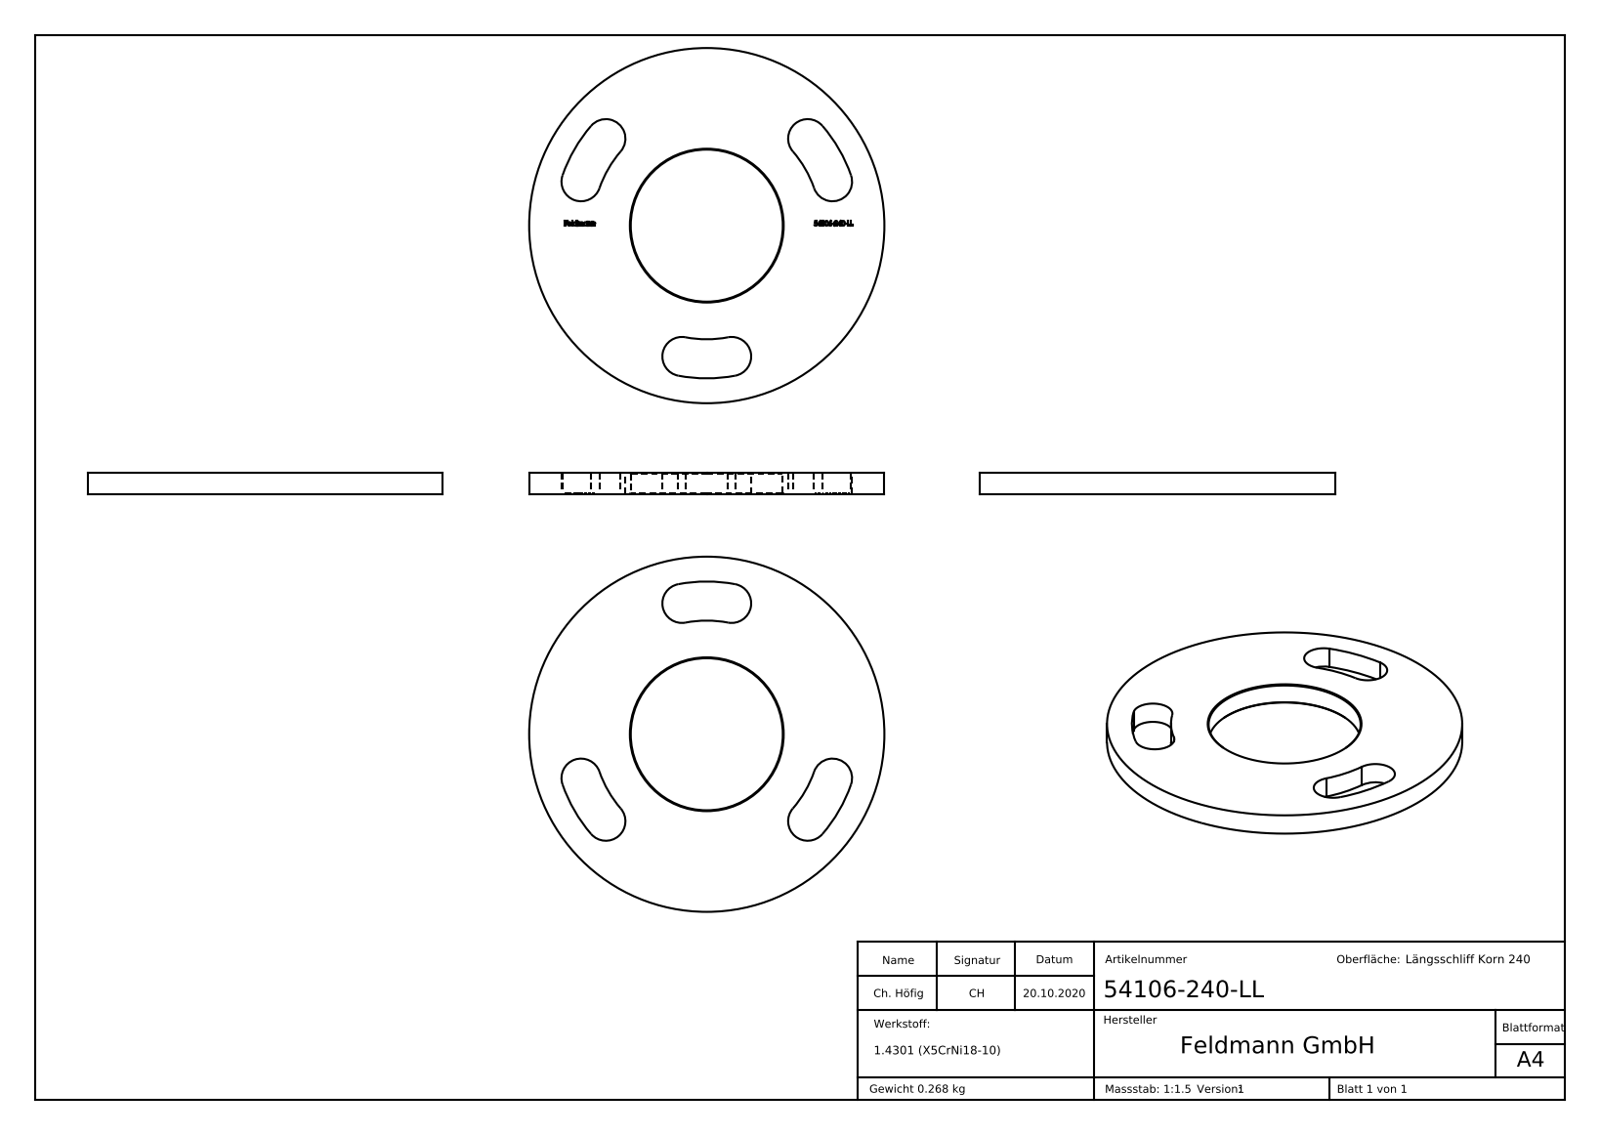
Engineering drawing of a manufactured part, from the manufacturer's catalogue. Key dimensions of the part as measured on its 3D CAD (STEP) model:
Part name (STEP PRODUCT): 54106-240-LL
STEP written by: SolidWorks 2018 (CONFIG_CONTROL_DESIGN)
Units: millimetres
Bodies: 1 solid, 264 faces (151 planar, 20 cylindrical, 93 other)
Overall size (bounding box): 100 × 100 × 6
Volume: 33 984 mm³ · Surface area: 15 123 mm²
Round holes (diameter × count): ⌀42.8 ×1
Round bosses / shafts (diameter × count): ⌀100 ×1
Partial cylindrical surfaces — rounded edges, fillets, slot ends (radius × count): R5.5 ×6, R32 ×1, R43 ×1
Main face-to-face distances: 6, 5.9, 0.44, 0.88, 0.85, 2.02, 77.66, 7.04, 7.89, 79.68
